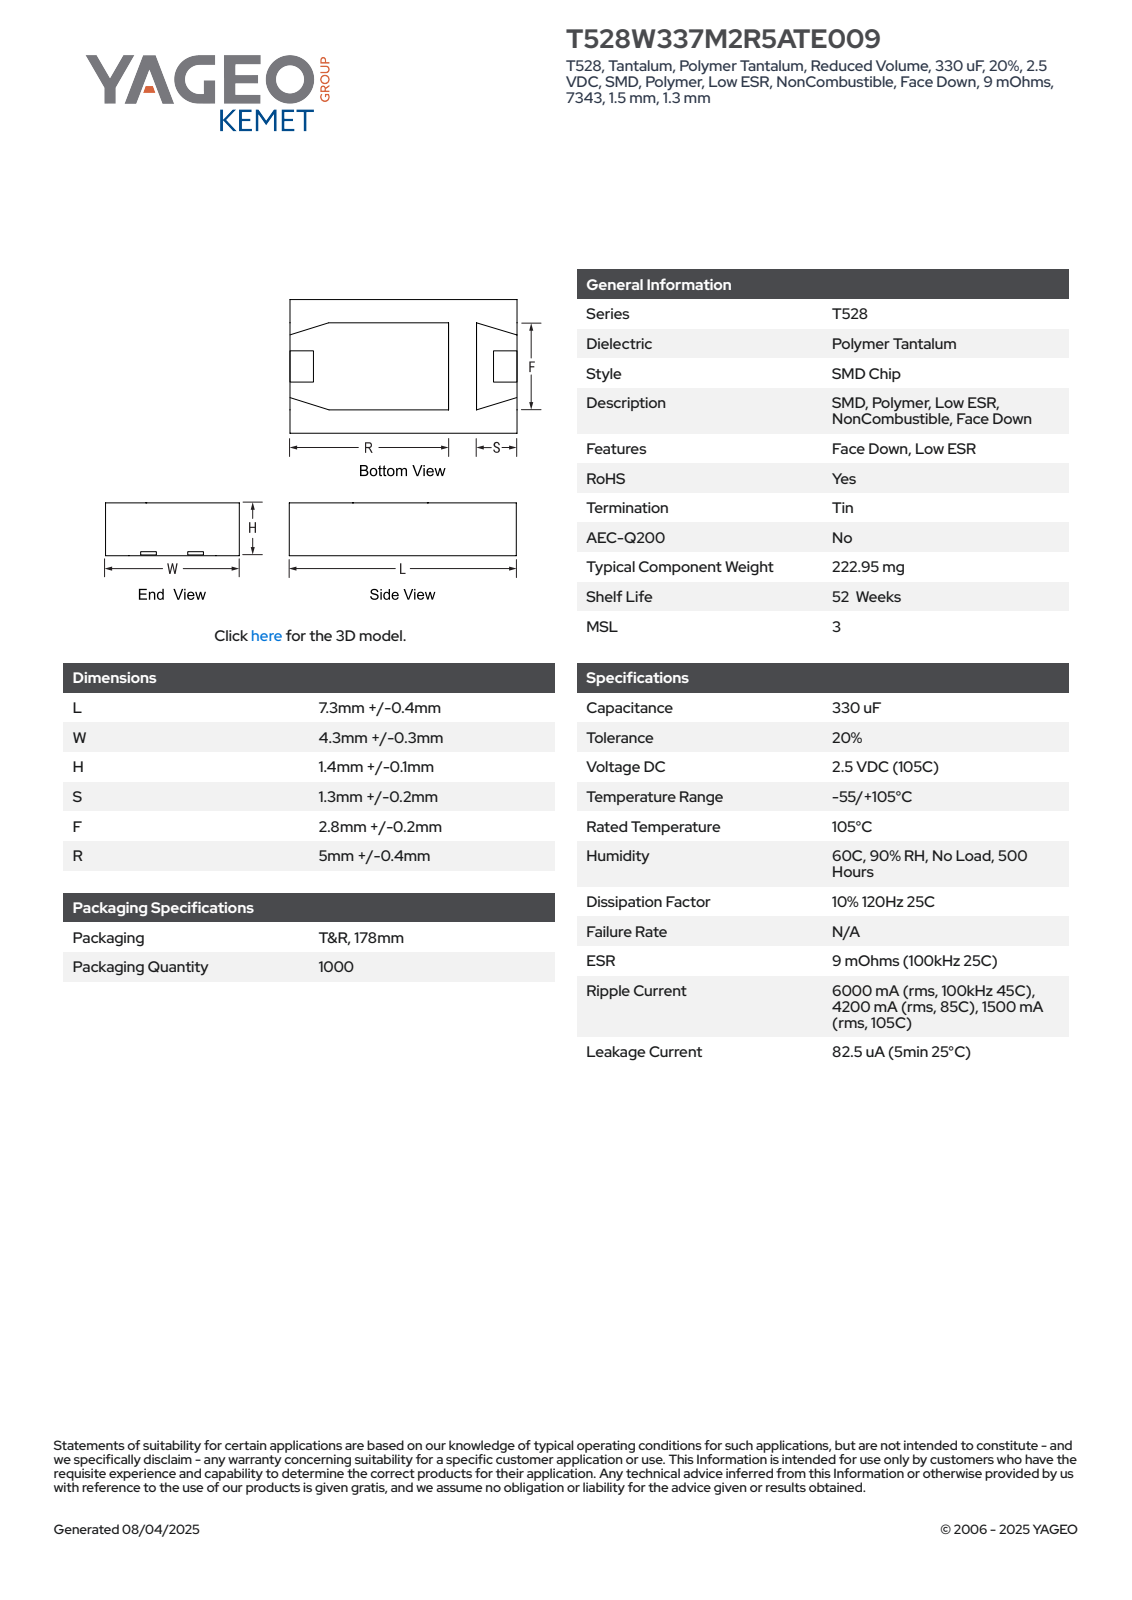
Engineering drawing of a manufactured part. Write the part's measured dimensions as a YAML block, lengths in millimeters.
part_name: "CTS_TWZ_7343_L7.7W4.6H1.5S1.5F3R5.4"
step_written_by: "SolidWorks 2014 (AUTOMOTIVE_DESIGN)"
units: millimeters
bodies: {solids: 4, faces: 100, planar: 100, cylindrical: 0, other: 0}
overall_size: [7.71, 4.6, 1.51]
volume: 53
surface_area: 114
face_to_face_distances: [1.51, 1.5, 4.6, 7.7, 1.52, 7.71, 7.72, 0.8, 3.8, 1.8]
